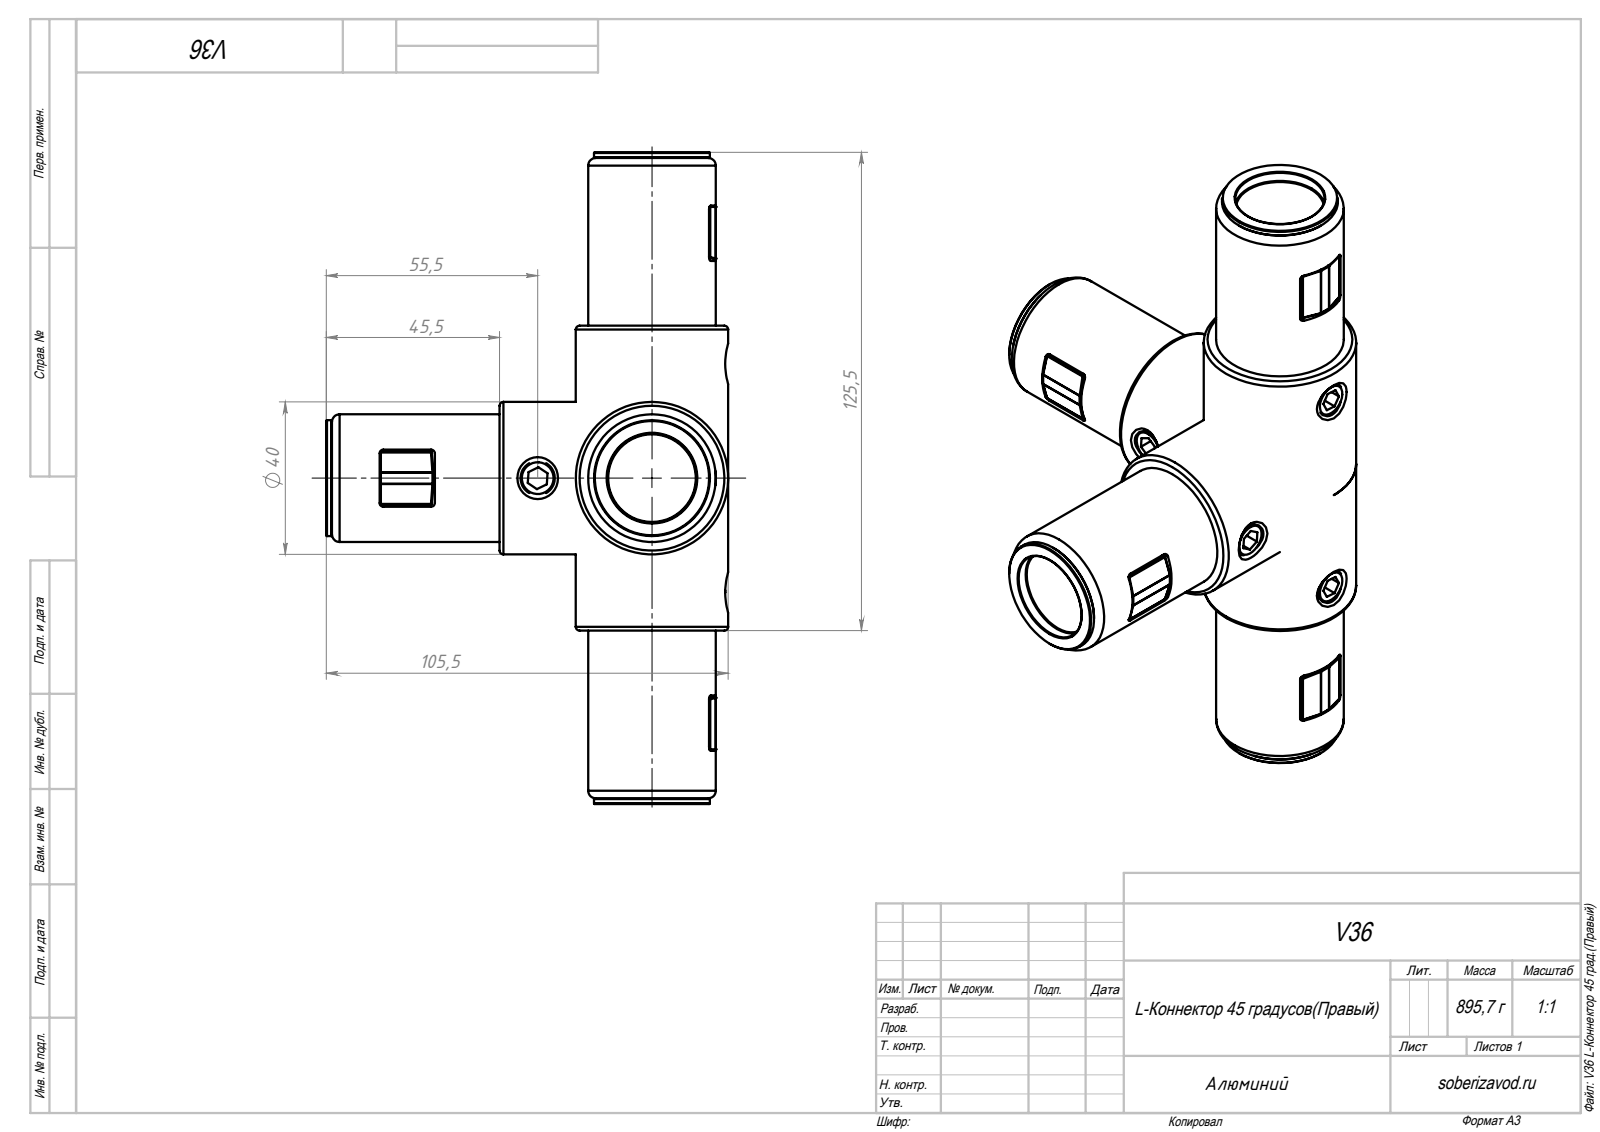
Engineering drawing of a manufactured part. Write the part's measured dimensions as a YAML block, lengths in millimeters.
part_name: "socket set screw cone point_din_DIN 914 - M10 x 12-N"
step_written_by: "SolidWorks 2018 (AUTOMOTIVE_DESIGN)"
units: millimeters
bodies: {solids: 16, faces: 789, planar: 175, cylindrical: 308, other: 306}
overall_size: [171, 105.5, 105.5]
volume: 294056
surface_area: 83682
round_holes:
  - {diameter: 9, count: 4}
  - {diameter: 14, count: 3}
  - {diameter: 23.4, count: 3}
  - {diameter: 26, count: 3}
round_bosses_or_shafts:
  - {diameter: 10, count: 4}
  - {diameter: 40, count: 3}
  - {diameter: 33.5, count: 3}
  - {diameter: 30.4, count: 3}
  - {diameter: 26.4, count: 3}
partial_cylinders:
  - {radius: 0.2, count: 110}
  - {radius: 1, count: 16}
face_to_face_distances: [1.5, 3, 27.5, 26, 29, 81, 82.5, 15, 55, 166.5]
hole_center_spacings: [30, 42.43, 60]
